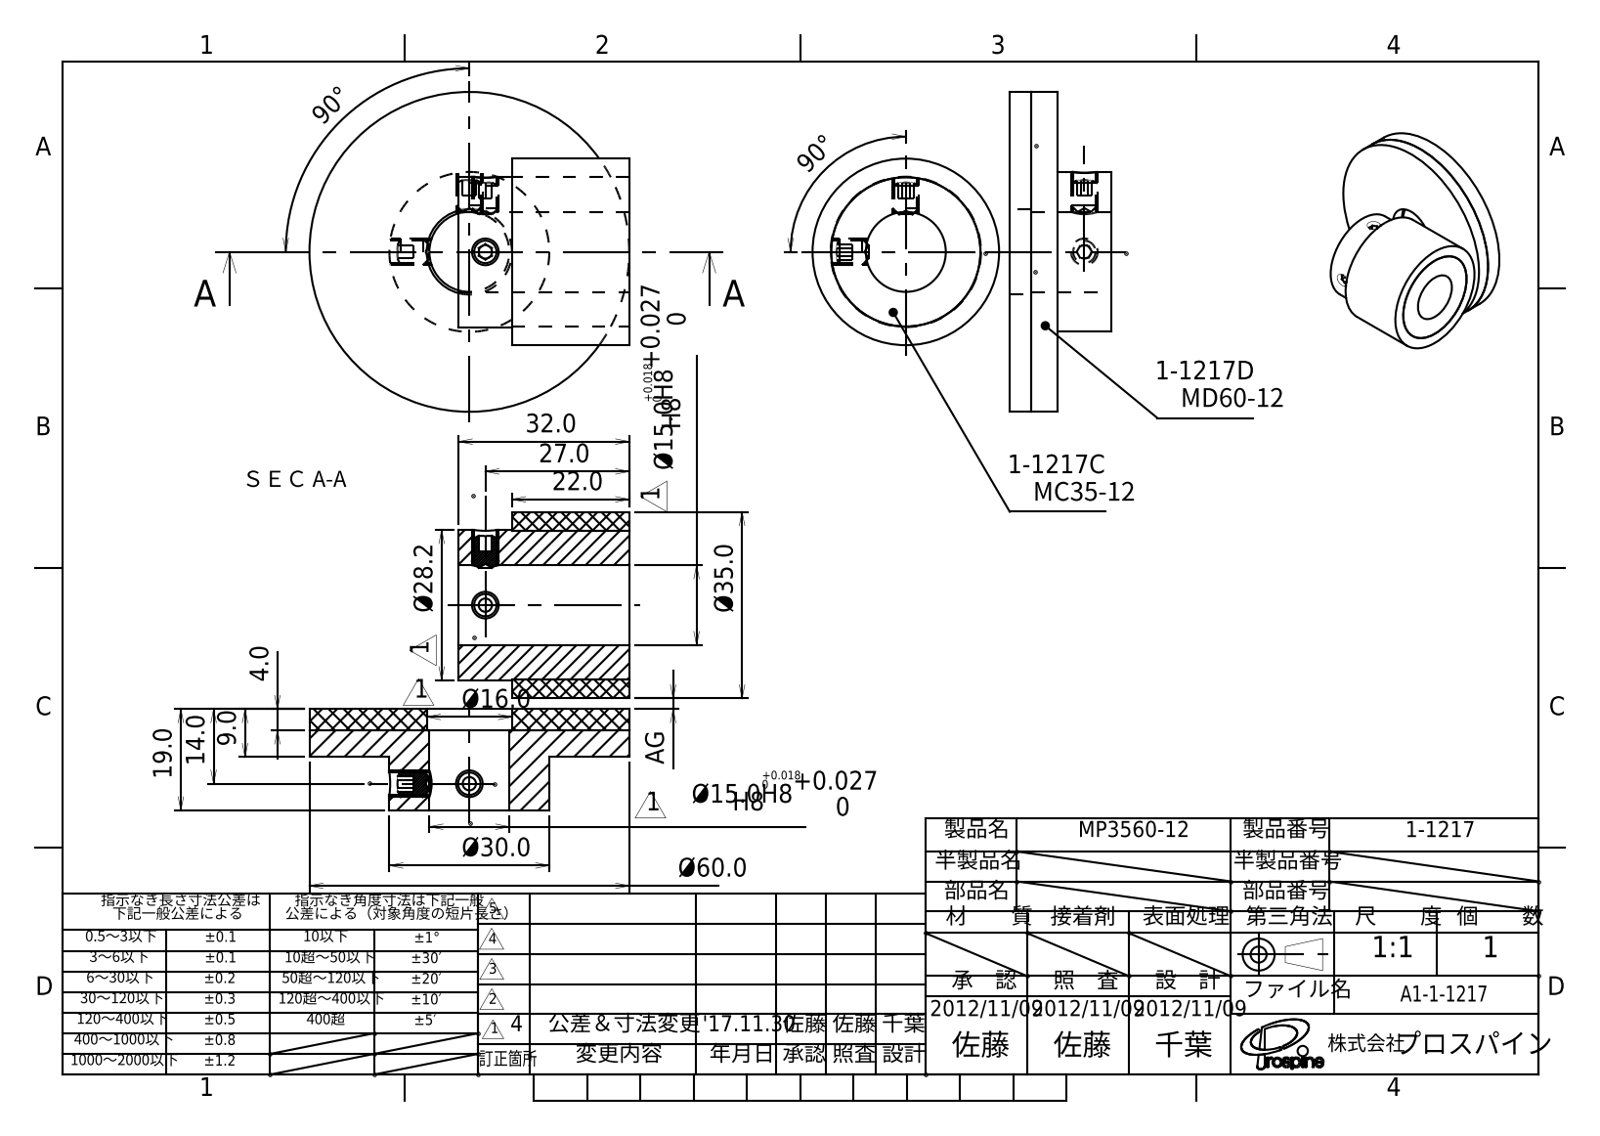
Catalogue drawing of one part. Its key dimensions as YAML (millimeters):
step_written_by: "PSStep 10.0 (CONFIG_CONTROL_DESIGN)"
units: millimeters
bodies: {solids: 12, faces: 112, planar: 66, cylindrical: 22, other: 24}
overall_size: [60, 60, 56]
volume: 51106
surface_area: 25744
round_holes:
  - {diameter: 4.2, count: 4}
  - {diameter: 15, count: 2}
  - {diameter: 16, count: 1}
  - {diameter: 28, count: 1}
round_bosses_or_shafts:
  - {diameter: 5, count: 4}
  - {diameter: 60, count: 1}
  - {diameter: 35, count: 1}
  - {diameter: 30, count: 1}
  - {diameter: 28.2, count: 1}
face_to_face_distances: [4, 5, 9, 10, 15, 19, 32, 22, 2.5, 2.49]
hole_center_spacings: [3, 33.5, 33.63]
